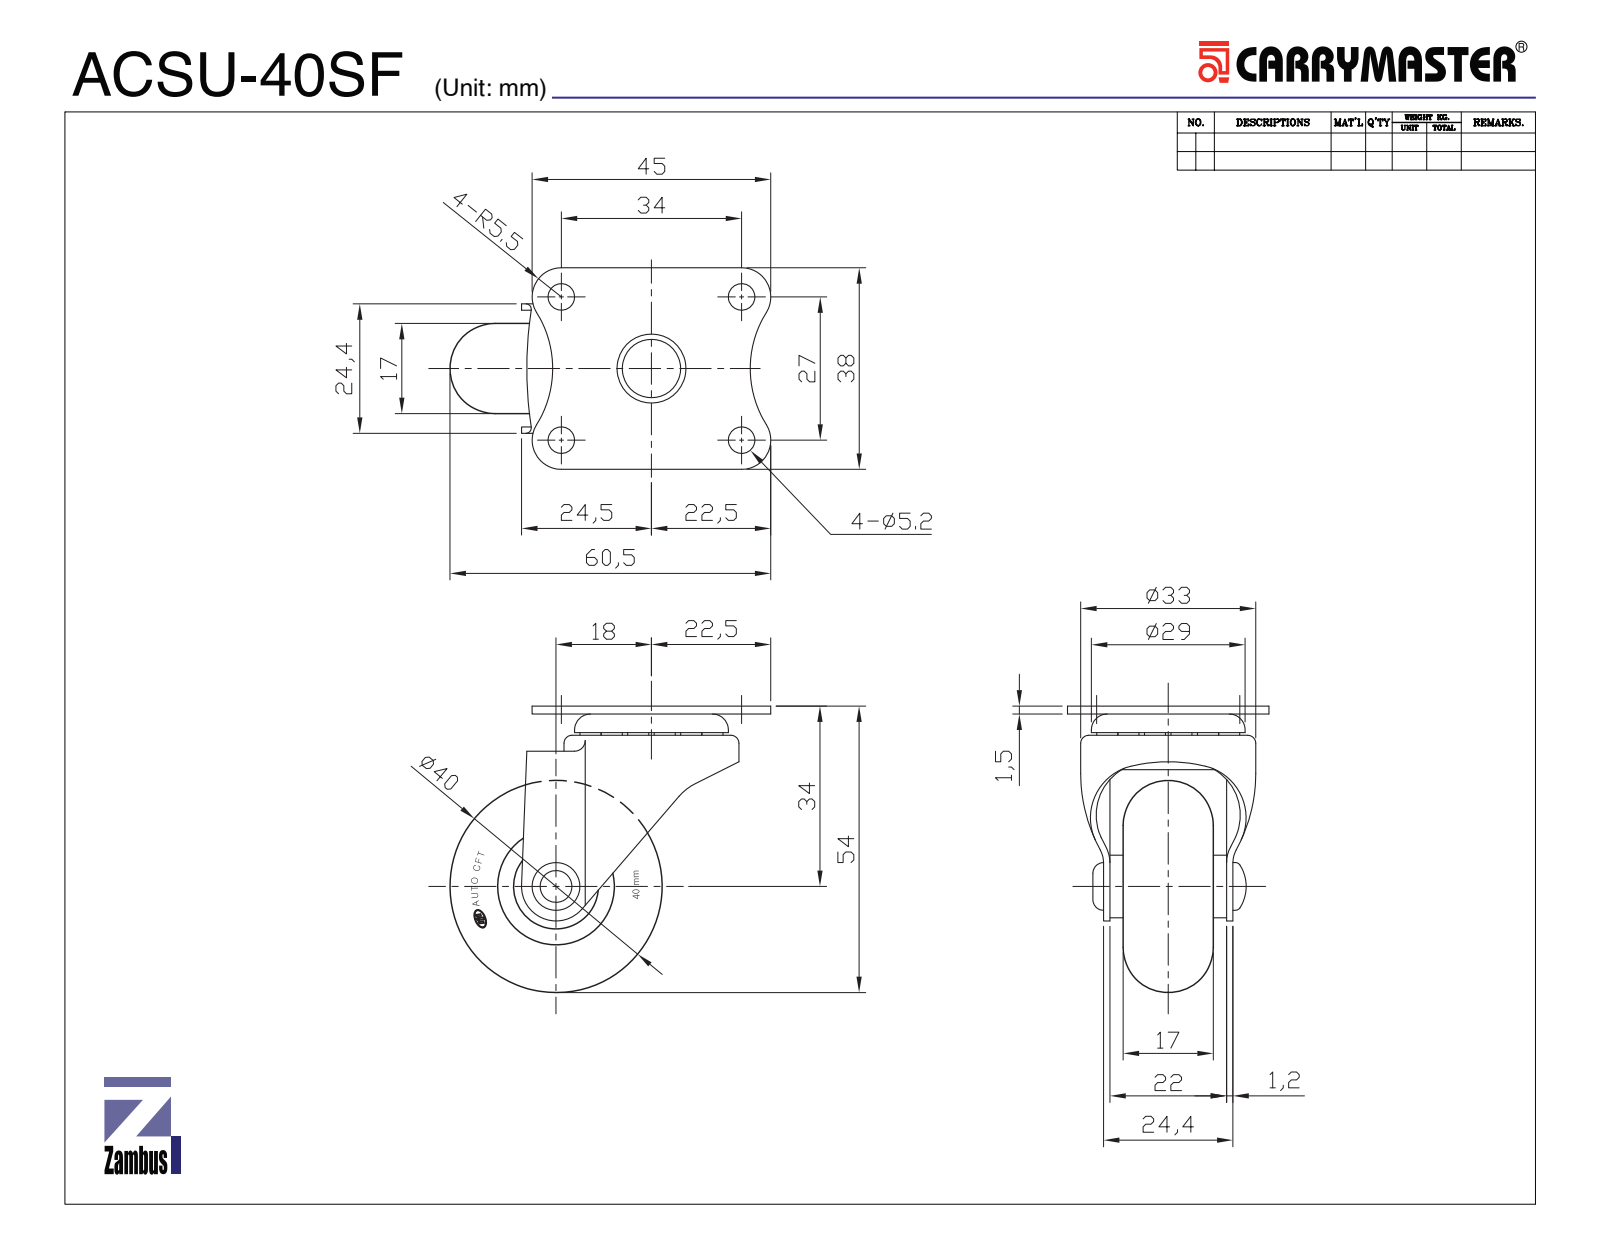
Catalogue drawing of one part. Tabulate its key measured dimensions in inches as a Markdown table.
| quantity | value |
| --- | --- |
| part name | ACSU-40SF BODY; 230-31-1; ACSU-40 WHEEL CORE; 230-01-1 (+8 more) |
| STEP written by | SolidWorks 2016 (CONFIG_CONTROL_DESIGN) |
| units | inches |
| bodies | 17 solids, 489 faces (83 planar, 180 cylindrical, 226 other) |
| overall size | 2.264 × 2.126 × 1.772 |
| volume | 1.666 in³ |
| surface area | 40.57 in² |
| round holes (diameter × count) | 0.205 × 4, 0.236 × 1, 0.276 × 1, 0.315 × 1, 0.407 × 1, 0.443 × 1, 0.512 × 1, 0.541 × 1, 0.63 × 1, 0.866 × 1, 1.043 × 1, 1.181 × 1 |
| round bosses / shafts (diameter × count) | 1.276 × 1, 1.142 × 1, 1.138 × 1, 0.63 × 1, 0.502 × 1, 0.433 × 1, 0.413 × 1, 0.404 × 1 |
| partial cylindrical surfaces (radius × count) | 0.039 × 32, 0.217 × 4, 0.079 × 2, 0.346 × 2, 0.394 × 2, 0.866 × 2, 0.276 × 1, 0.531 × 1 |
| main face-to-face distances | 0.059, 0.047, 0.098, 0.146, 0.768, 0.815, 0.913, 0.276, 0.669, 0.094 |
| hole center spacings | 0.855, 1.063, 1.339, 1.709 |
